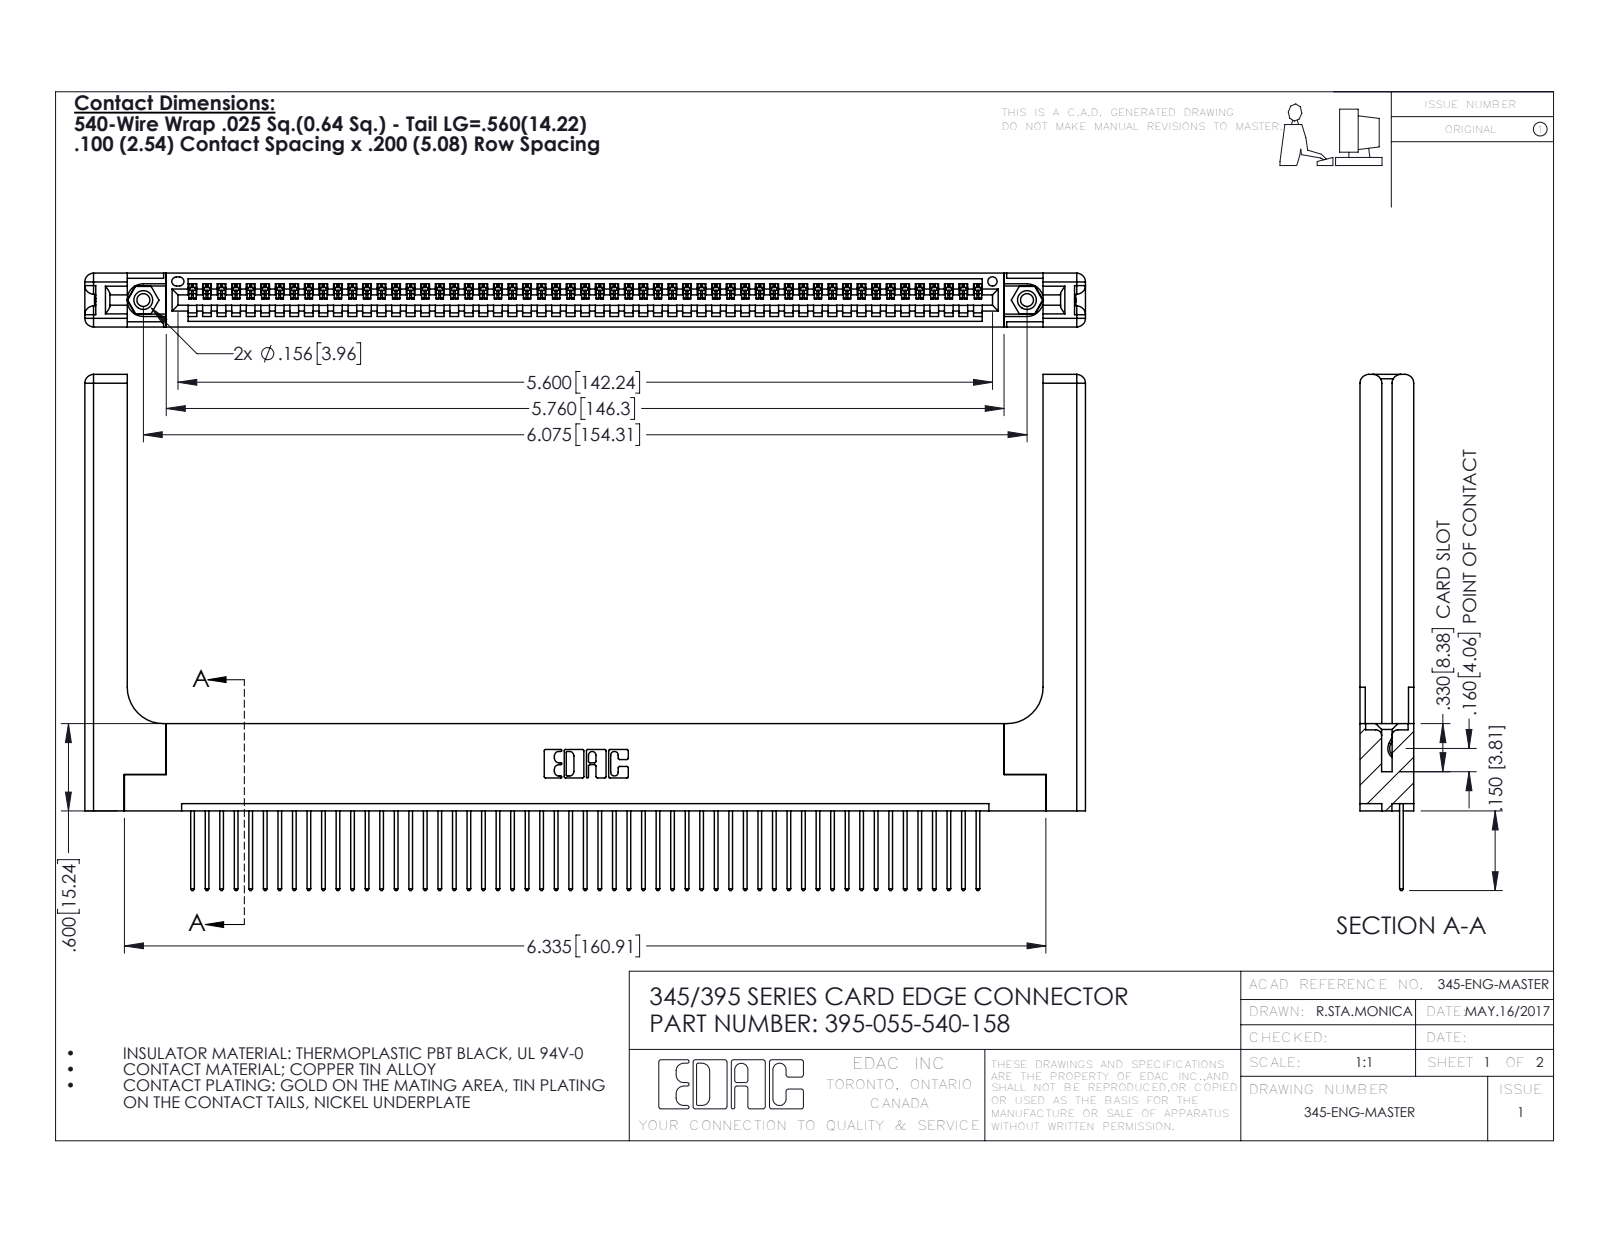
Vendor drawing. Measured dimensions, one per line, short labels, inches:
name: 345-250-001_345-250-001-102; 345-292-001_345-293-140; 395-055-540-158; 345 Part_Flush Mounting Lugs - 0.156 Dia-TH (+1 more)
written by: SolidWorks 2016 (CONFIG_CONTROL_DESIGN)
unit: in
bodies: 60 solids, 3572 faces (2428 planar, 1084 cylindrical, 60 other)
size: 6.879 × 3.547 × 0.37
volume: 1.543 in³; area: 43.89 in²
holes: 2× ⌀0.089, 2× ⌀0.125, 2× ⌀0.156, 1× ⌀0.064
bosses: 2× ⌀0.155
rounds: 110× R0.006, 110× R0.01, 22× R0.01, 16× R0.06, 6× R0.007, 6× R0.031, 3× R0.026, 2× R0.03
face distances: 0.072, 0.298, 0.37, 0.098, 0.272, 0.025, 0.2, 0.225, 0.148, 0.15
hole spacings: 0.27, 5.839, 6.075
